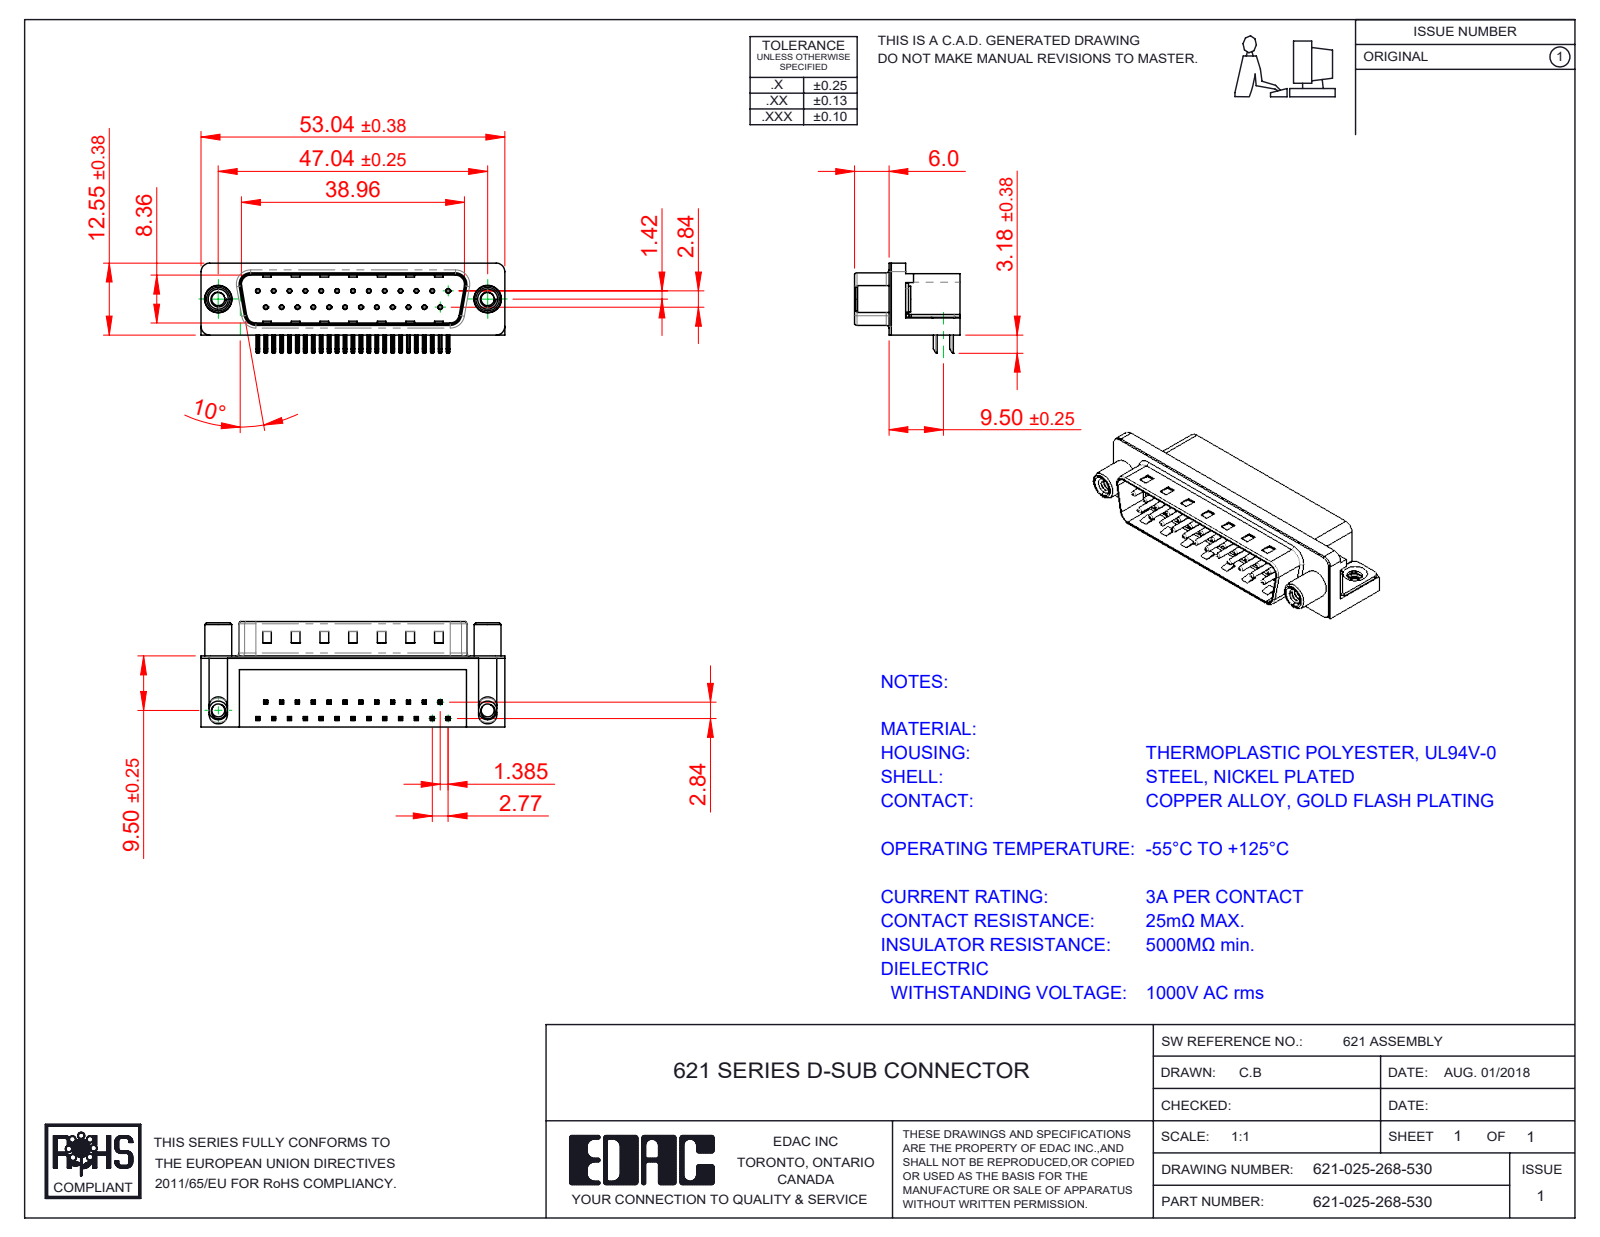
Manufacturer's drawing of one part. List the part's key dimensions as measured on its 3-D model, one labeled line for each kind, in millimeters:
Part name (STEP PRODUCT): 621 Contact Top; 621 Contact Bottom; 621 Shell_25 Socket; 621-025-268-530 (+3 more)
STEP written by: SolidWorks 2016 (CONFIG_CONTROL_DESIGN)
Units: millimetres
Bodies: 31 solids, 2297 faces (1429 planar, 675 cylindrical, 193 other)
Overall size (bounding box): 53.04 × 18.4 × 16.25
Volume: 6 437 mm³ · Surface area: 7 888 mm²
Round holes (diameter × count): ⌀0.35 ×25, ⌀0.8 ×25, ⌀2.3 ×2, ⌀3.1 ×2, ⌀4 ×2, ⌀4.8 ×2, ⌀5 ×2
Round bosses / shafts (diameter × count): ⌀0.75 ×25, ⌀4.9 ×2, ⌀4.7 ×2, ⌀4.5 ×2, ⌀3.85 ×2
Partial cylindrical surfaces — rounded edges, fillets, slot ends (radius × count): R0.25 ×100, R0.12 ×50, R1 ×16, R0.5 ×14, R1.6 ×8, R1.5 ×7, R0.32 ×4, R0.9 ×4
Main face-to-face distances: 0.4, 12, 10.35, 2.1, 8.76, 10.46, 1.7, 10.86, 12.4, 9
Hole centre spacings: 3.16, 2.77, 5.54, 8.31, 11.08, 13.85, 16.62, 5.03
